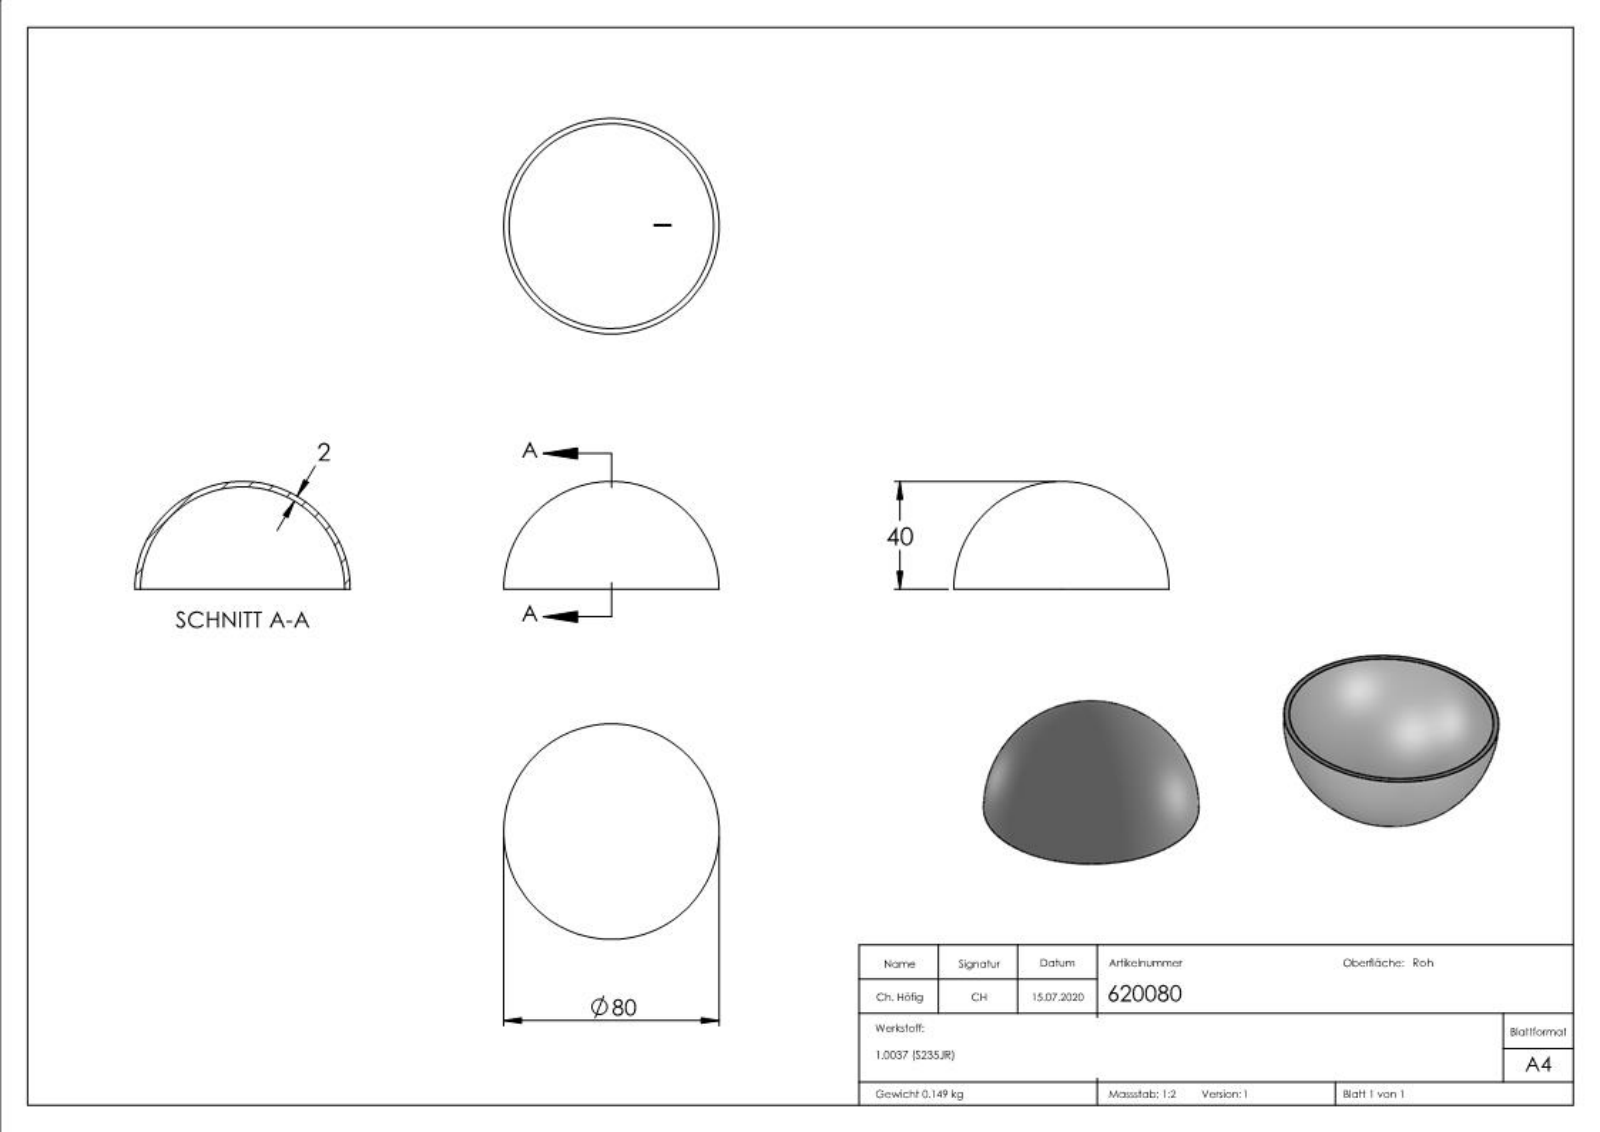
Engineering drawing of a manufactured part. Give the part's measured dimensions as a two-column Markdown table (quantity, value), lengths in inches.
| quantity | value |
| --- | --- |
| part name | 620080 |
| STEP written by | SolidWorks 2018 (CONFIG_CONTROL_DESIGN) |
| units | inches |
| bodies | 1 solid, 196 faces (64 planar, 0 cylindrical, 132 other) |
| overall size | 3.15 × 3.15 × 1.575 |
| volume | 1.167 in³ |
| surface area | 30.41 in² |
| main face-to-face distances | 0.047, 0.022, 0.02, 0.032, 0.018, 0.026, 0.069, 0.052, 0.021, 0.058 |
